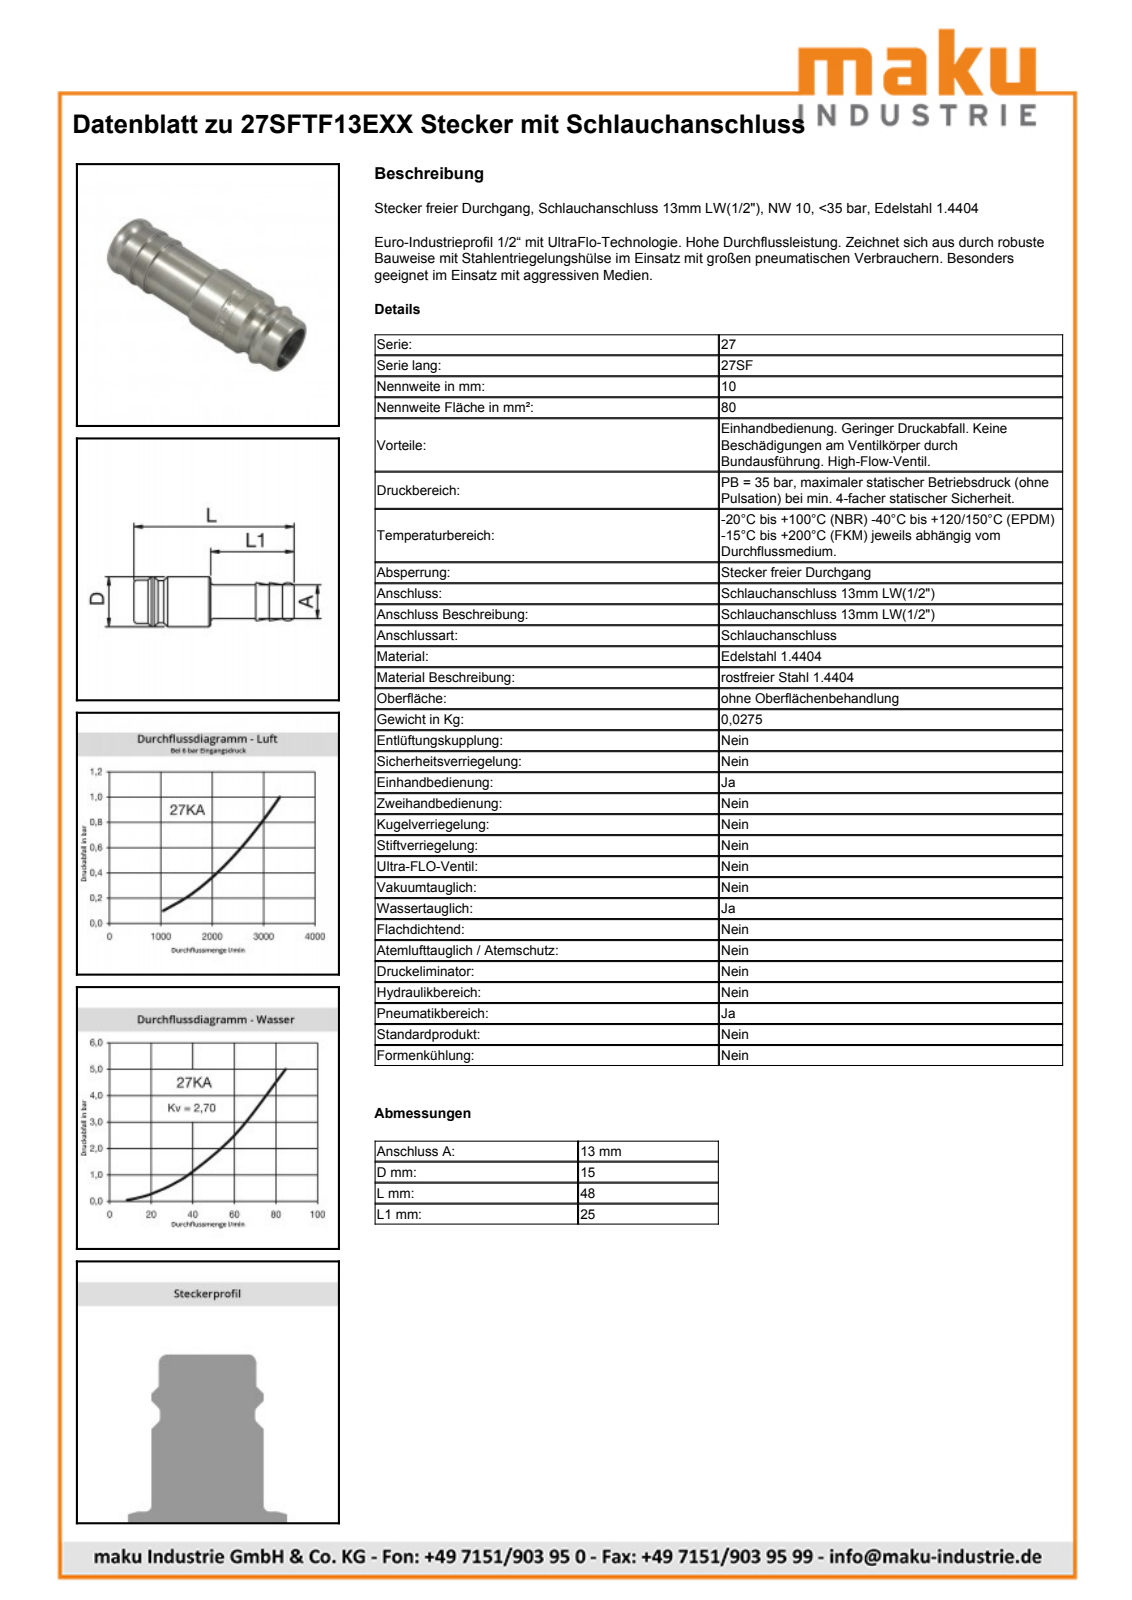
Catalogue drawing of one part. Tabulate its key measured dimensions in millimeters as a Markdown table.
| quantity | value |
| --- | --- |
| part name | D106658 |
| STEP written by | Autodesk Inventor 2011 (AUTOMOTIVE_DESIGN) |
| units | millimeters |
| bodies | 1 solid, 25 faces (4 planar, 6 cylindrical, 15 other) |
| overall size | 48 × 15 × 15 |
| volume | 3 484 mm³ |
| surface area | 3 806 mm² |
| round holes (diameter × count) | 10 × 1 |
| round bosses / shafts (diameter × count) | 15 × 1, 13.1 × 1, 13 × 1, 12.65 × 1 |
| main face-to-face distances | 48, 36.5, 11.5, 40.5, 4, 7.5 |
